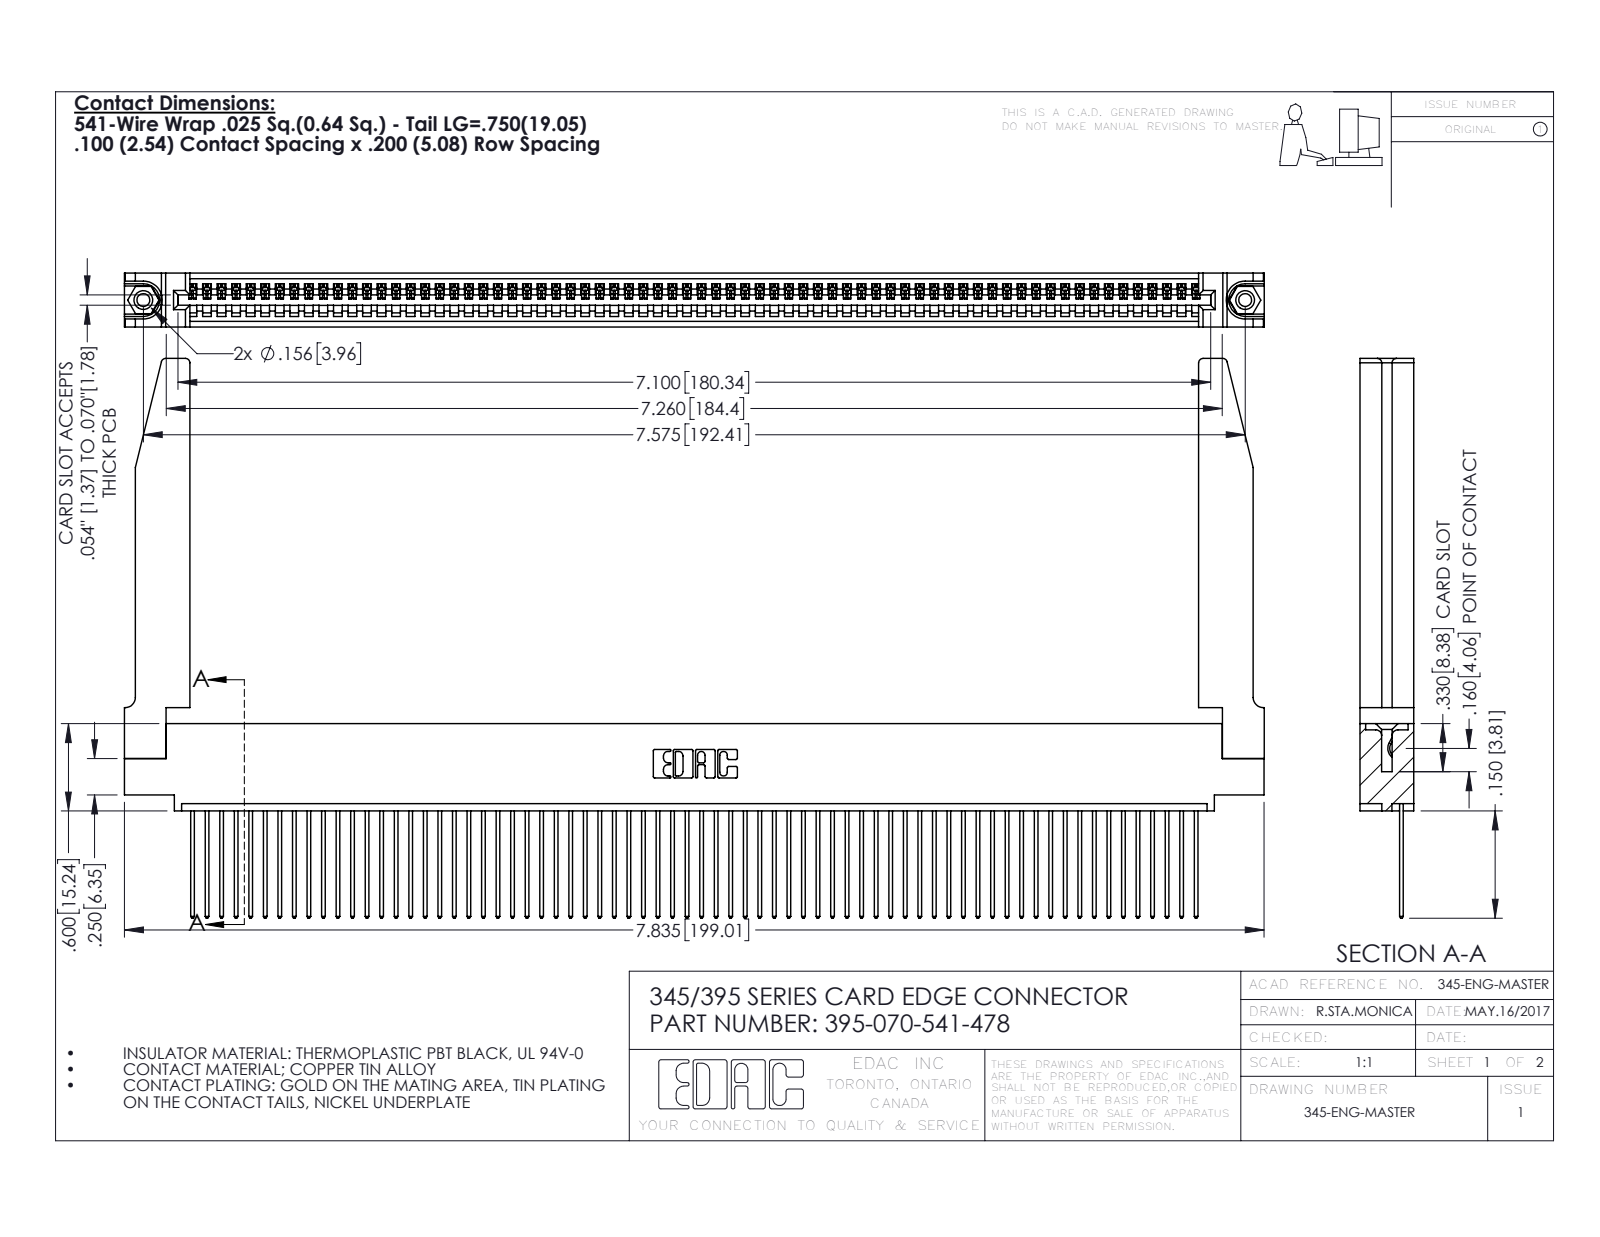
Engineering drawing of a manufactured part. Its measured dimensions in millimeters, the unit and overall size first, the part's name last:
Units: millimetres
Overall size (bounding box): 199 × 97.7 × 9.4
Round holes (diameter × count): ⌀2.3 ×2, ⌀3.2 ×2, ⌀4 ×2, ⌀1.6 ×1
Round bosses / shafts (diameter × count): ⌀3.9 ×2
Partial cylindrical surfaces — rounded edges, fillets, slot ends (radius × count): R0.2 ×140, R0.3 ×140, R0.3 ×22, R0.8 ×8, R0.2 ×6, R0.8 ×6, R0.7 ×3, R0.8 ×2
Main face-to-face distances: 1.8, 7.6, 9.4, 2.5, 6.9, 0.6, 5.1, 5.7, 3.8, 3.8
Hole centre spacings: 6.9, 186.4, 192.4
Volume: 27 060 mm³ · Surface area: 34 300 mm²
Bodies: 75 solids, 4424 faces (3026 planar, 1346 cylindrical, 52 other)
Part name (STEP PRODUCT): 345-292-001_345-293-141; 345-250-001_345-250-001-102; 345 Part_0.110 Offset - 0.156 Dia-TH; 395-070-541-478 (+1 more)
STEP written by: SolidWorks 2016 (CONFIG_CONTROL_DESIGN)
